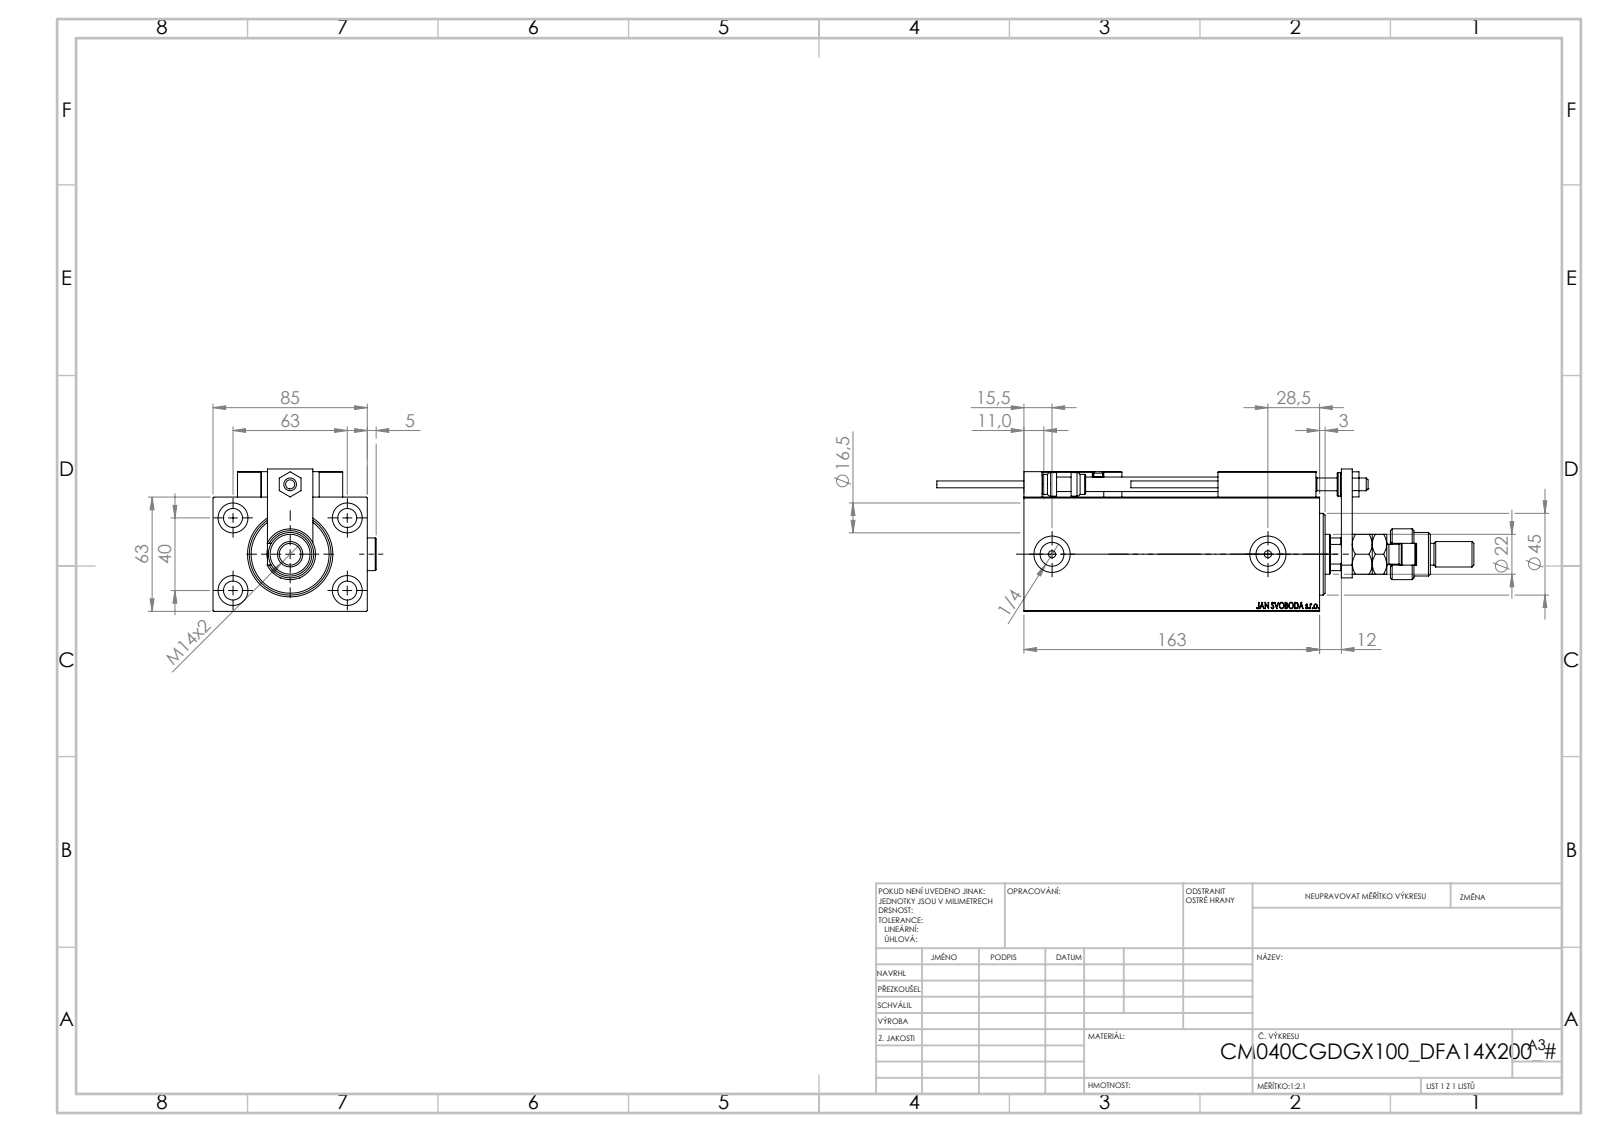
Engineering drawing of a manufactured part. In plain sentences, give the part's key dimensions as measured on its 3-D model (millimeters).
The part is named "FEMALE_PART_FOR_DFA; V450CM_VC_B; V450CM_C_Body; KONCOVKA (+8 more)". Its 3-D file was written by "SolidWorks 2019 (CONFIG_CONTROL_DESIGN)". It is 25 solids with 1381 faces: 592 planar, 211 cylindrical and 578 other. Overall it measures 296 by 85 by 78.5 millimeters. Its volume is 788 552 cubic millimeters and its surface area 154 103 square millimeters. Round holes: 6 of diameter 4, 5 of diameter 8, 5 of diameter 16.5, 4 of diameter 3.2, 4 of diameter 10.5, 2 of diameter 5, 2 of diameter 13.16, 2 of diameter 20, 1 of diameter 7, 1 of diameter 12.5, 1 of diameter 22, 1 of diameter 25.5. Round bosses or shafts: 2 of diameter 11, 2 of diameter 5, 2 of diameter 3.8, 1 of diameter 28, 1 of diameter 24, 1 of diameter 18, 1 of diameter 14, 1 of diameter 13. Partial cylindrical surfaces (rounded edges, fillets, slot ends): 30 of radius 0.3, 2 of radius 3, 1 of radius 9.75, 1 of radius 10.5. The main face-to-face distances are 63, 85, 14, 163, 128.25, 34.75, 10, 13, 18, 77. The hole center spacings are 37.31, 11.37, 20, 29.59, 29.69, 36.06, 36.53, 40.
